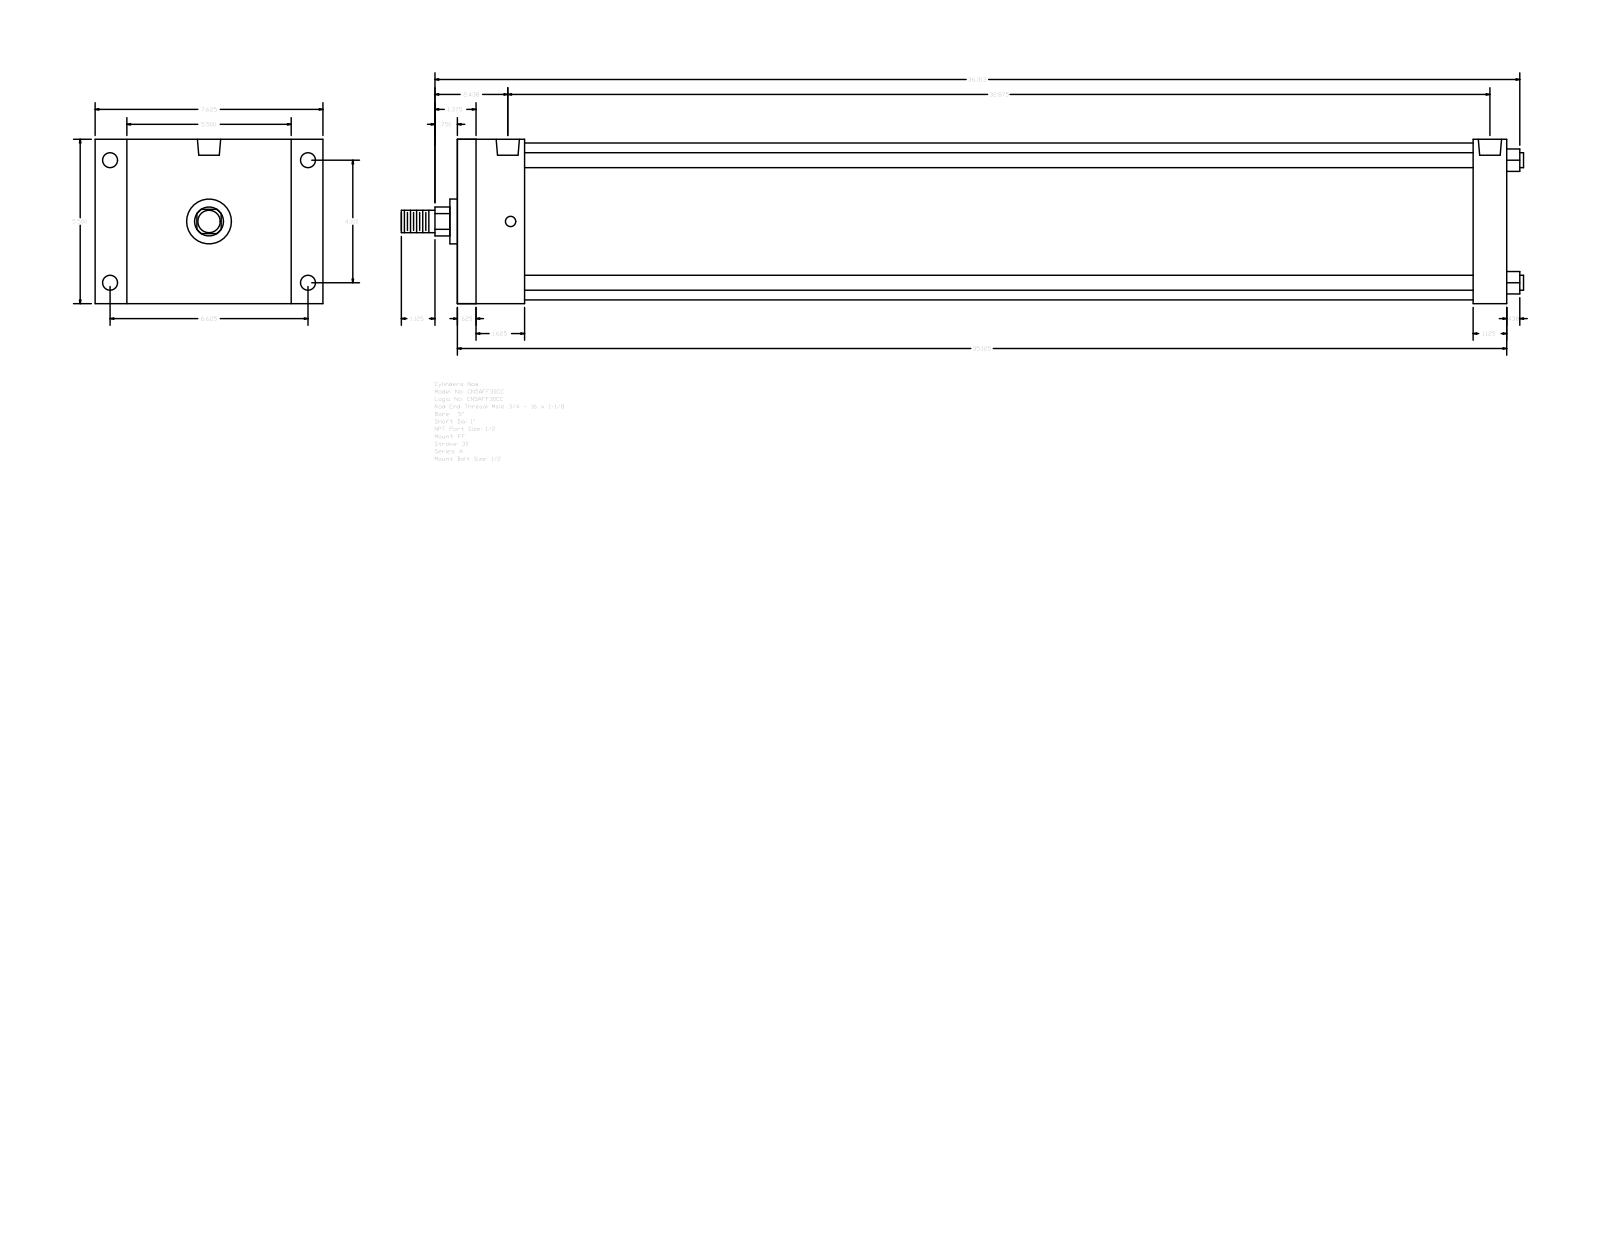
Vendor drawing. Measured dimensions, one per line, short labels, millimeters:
name: A_FF__0500_1
written by: GSSL Pune (CONFIG_CONTROL_DESIGN)
unit: mm
bodies: 0 solids, 92 faces (64 planar, 28 cylindrical, 0 other)
size: 954.09 × 193.68 × 139.7
holes: 4× ⌀8.73, 4× ⌀12.7, 2× ⌀19.77
bosses: 4× ⌀12.7, 1× ⌀133.35, 1× ⌀38.1, 1× ⌀25.4, 1× ⌀19.05
rounds: 1× R12.29
face distances: 139.7, 892.18, 15.87, 876.31, 863.6, 847.73, 28.58, 57.15, 41.28, 806.45
hole spacings: 2.39, 104.14, 168.28, 197.9, 830.25, 832.64, 835.03
